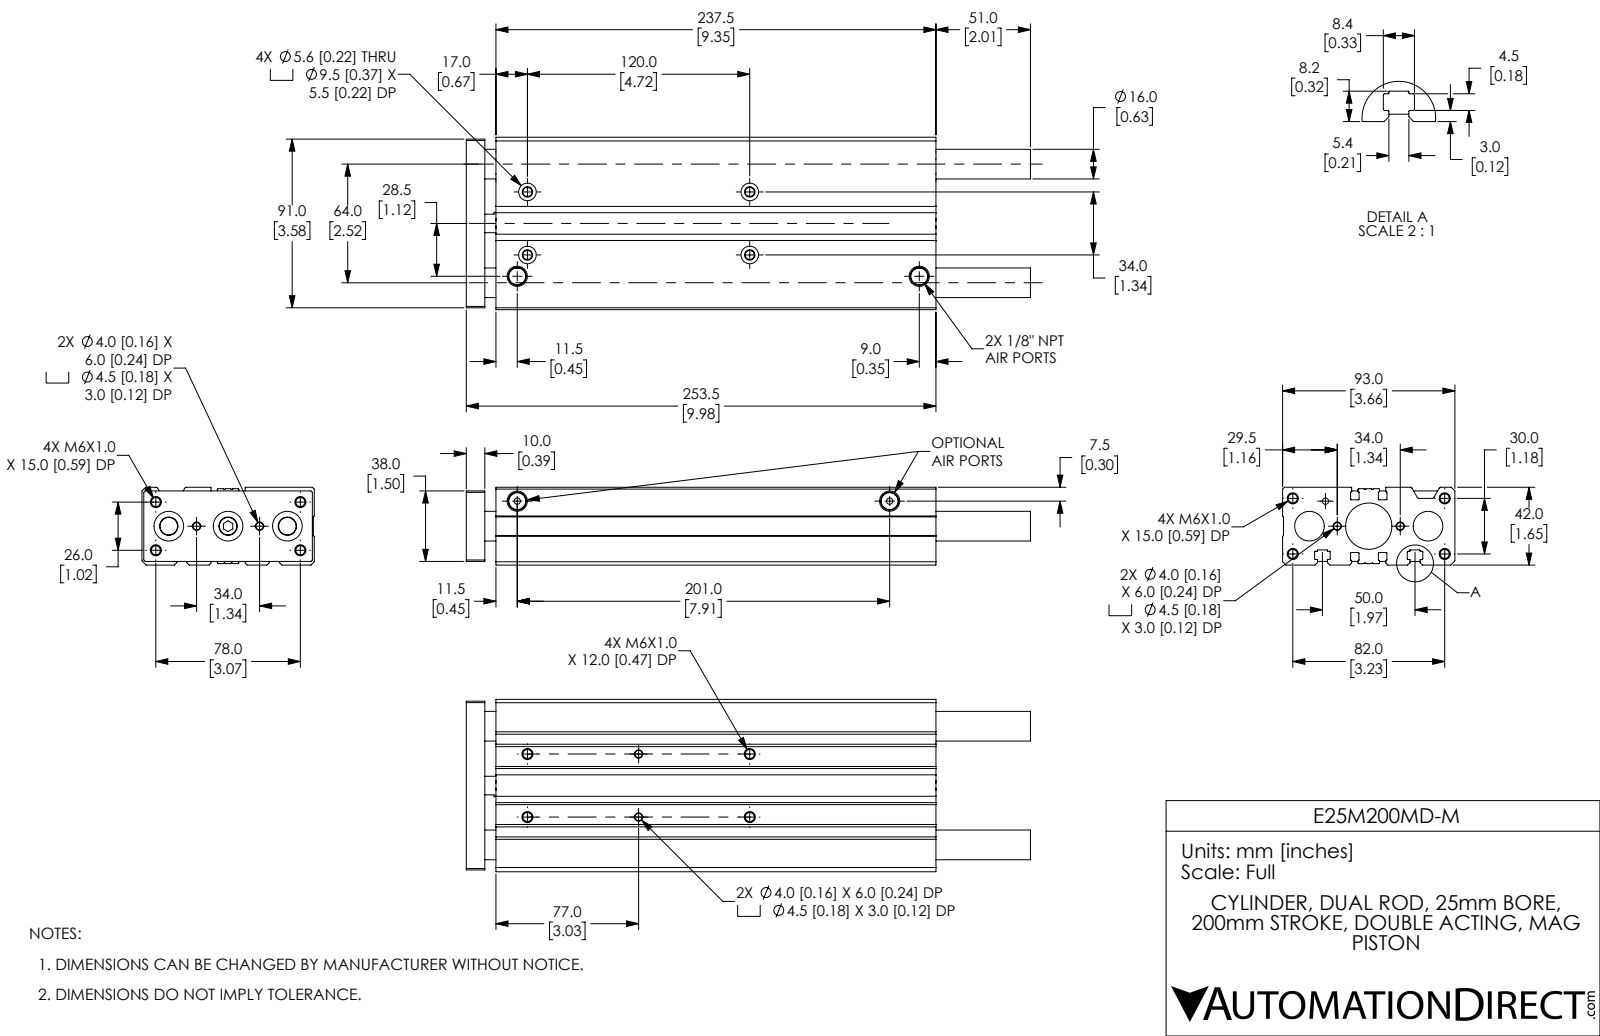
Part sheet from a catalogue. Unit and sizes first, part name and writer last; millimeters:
Units: millimetres
Overall size (bounding box): 304.5 × 93 × 42
Round holes (diameter × count): ⌀4.92 ×10, ⌀4 ×4, ⌀4.5 ×4, ⌀5.6 ×4, ⌀9.5 ×4, ⌀8 ×3, ⌀16 ×3, ⌀3.43 ×2, ⌀4.92 ×2, ⌀9.91 ×2, ⌀3.43 ×1, ⌀16 ×1
Round bosses / shafts (diameter × count): ⌀12 ×1, ⌀9.91 ×1
Partial cylindrical surfaces — rounded edges, fillets, slot ends (radius × count): R0.2 ×32, R0.4 ×28, R1 ×4, R0.3 ×2
Main face-to-face distances: 42, 6, 93, 0.8, 34.4, 15, 35.2, 41.2, 6.8, 41.3
Hole centre spacings: 2.83, 14.76, 17.49, 25.55, 28.07, 28.3, 34, 41.11
Volume: 817 855 mm³ · Surface area: 195 780 mm²
Bodies: 5 solids, 423 faces (139 planar, 190 cylindrical, 94 other)
Part name (STEP PRODUCT): E25M200MD-M_ENDPLATE; E25M200MD-M; E25M200MD-M_BODY
STEP written by: SolidWorks 2019 (CONFIG_CONTROL_DESIGN)
